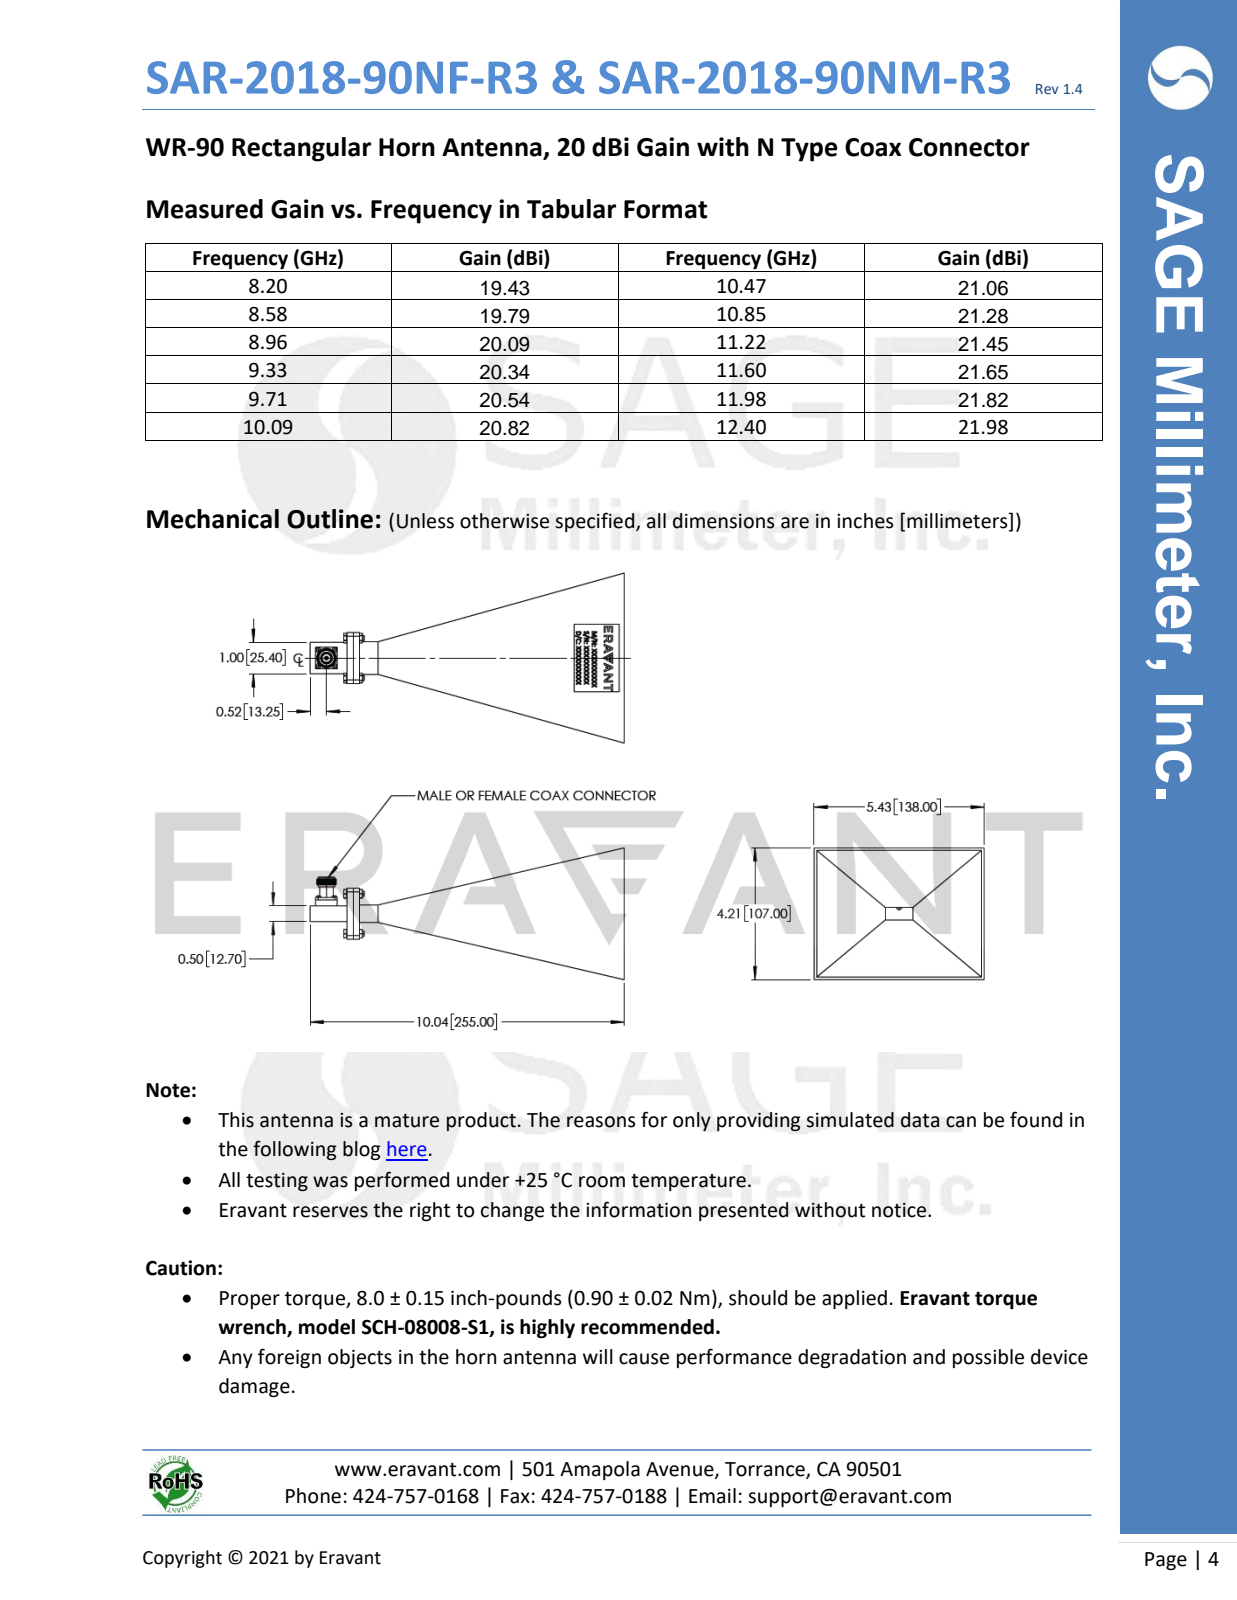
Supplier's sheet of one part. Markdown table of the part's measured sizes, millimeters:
| quantity | value |
| --- | --- |
| part name | SAR-2018-90NF-R3, Defeatured |
| STEP written by | SolidWorks 2021 (CONFIG_CONTROL_DESIGN) |
| units | millimeters |
| bodies | 0 solids, 426 faces (179 planar, 119 cylindrical, 128 other) |
| overall size | 255 × 138 × 107 |
| round holes (diameter × count) | 3 × 4 |
| round bosses / shafts (diameter × count) | 4 × 8, 3.5 × 4, 2.5 × 4, 2 × 4, 15.9 × 1, 13.5 × 1, 11 × 1 |
| partial cylindrical surfaces (radius × count) | 0.3 × 24, 0.5 × 24, 2 × 4, 3 × 4 |
| main face-to-face distances | 224.7, 10, 214.8, 215, 225, 8, 0.8, 13.5, 14.4, 33.4 |
| hole center spacings | 12.7, 18 |
